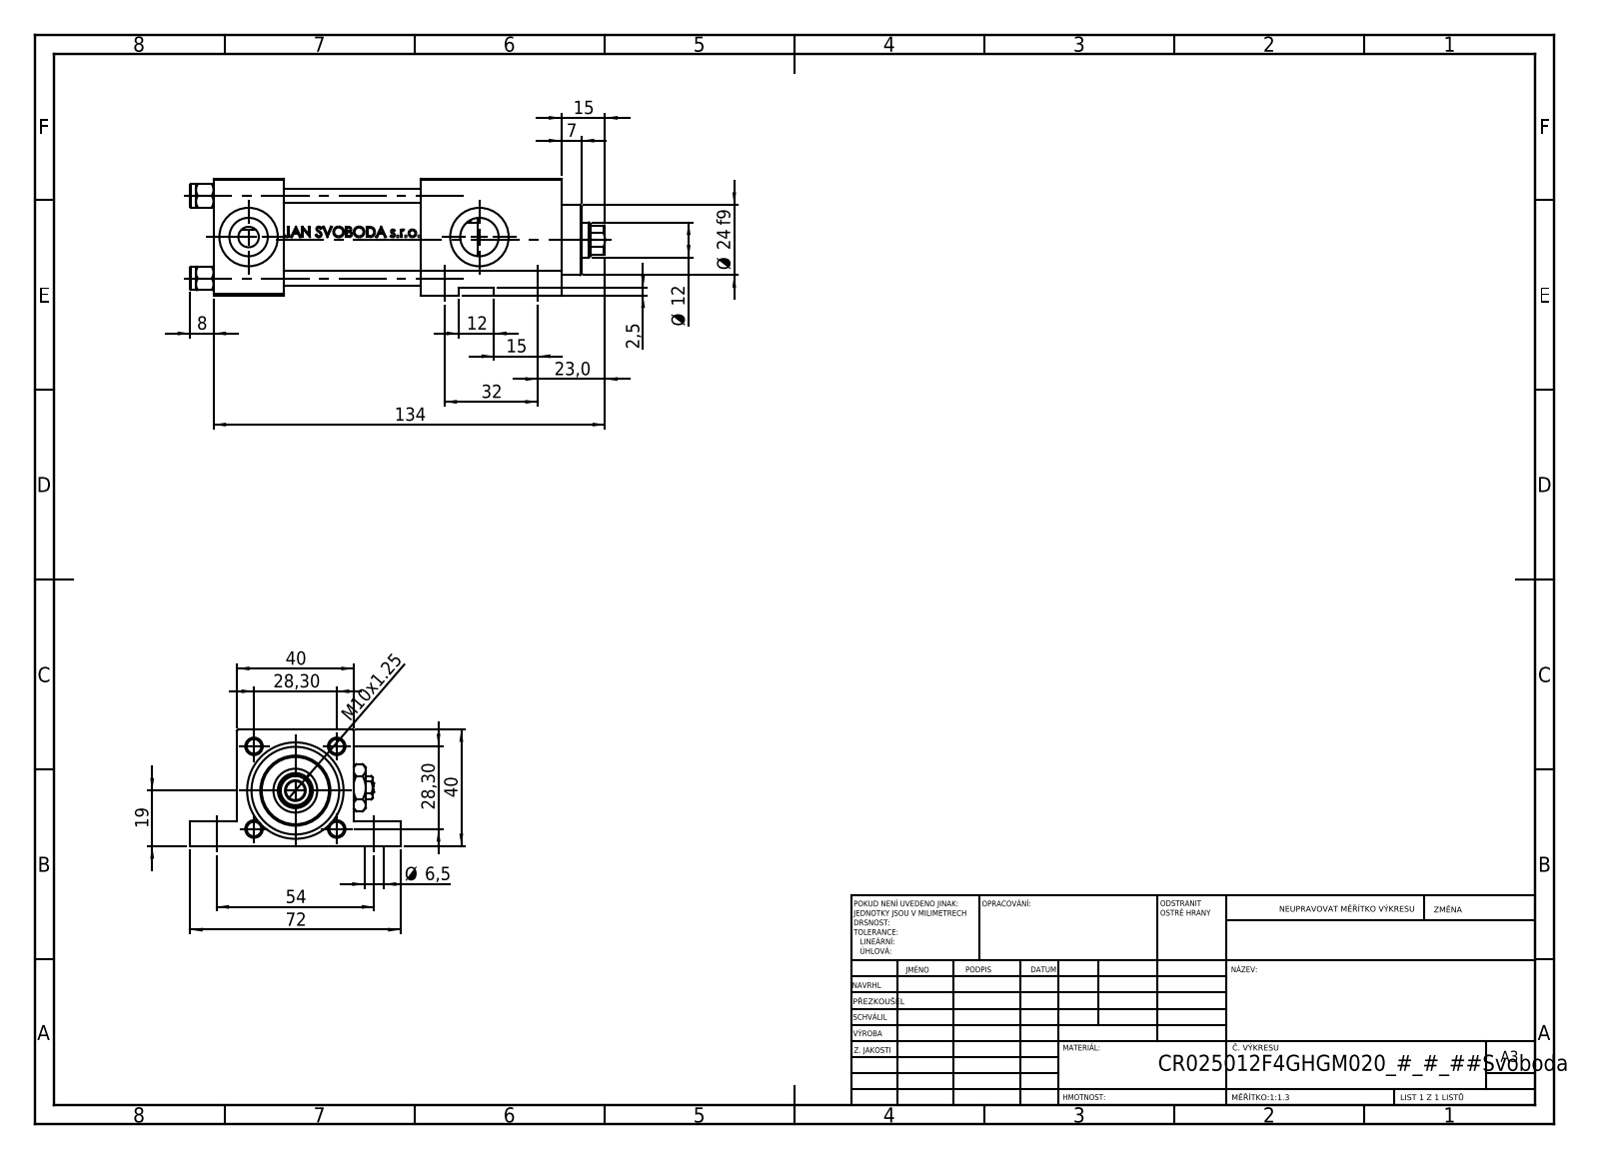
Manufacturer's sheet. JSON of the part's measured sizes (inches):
{"part_name": "V215_VC_A; NUT_M5_F; Zatka_pro_OIL_PORT; V215CR_F_Body (+2 more)", "step_written_by": "SolidWorks 2019 (CONFIG_CONTROL_DESIGN)", "units": "inches", "bodies": {"solids": 12, "faces": 1150, "planar": 460, "cylindrical": 130, "other": 560}, "overall_size": [5.591, 2.835, 1.575], "volume_in3": 9.267, "surface_area_in2": 91.74, "round_holes": [[0.256, 5], [0.197, 4], [0.787, 4], [0.518, 3], [0.276, 2], [0.472, 1], [0.591, 1], [0.984, 1], [1.181, 1]], "round_bosses_or_shafts": [[0.315, 4], [1.22, 1], [0.945, 1]], "partial_cylinders_radius": [[0.217, 1]], "face_to_face_distances": [1.575, 0.945, 0.335, 1.24, 1.89, 1.85, 2.795, 4.685, 3.74, 0.236], "hole_center_spacings": [1.114, 0.761, 0.816, 1.26, 1.576, 2.126, 2.471, 0.276]}
